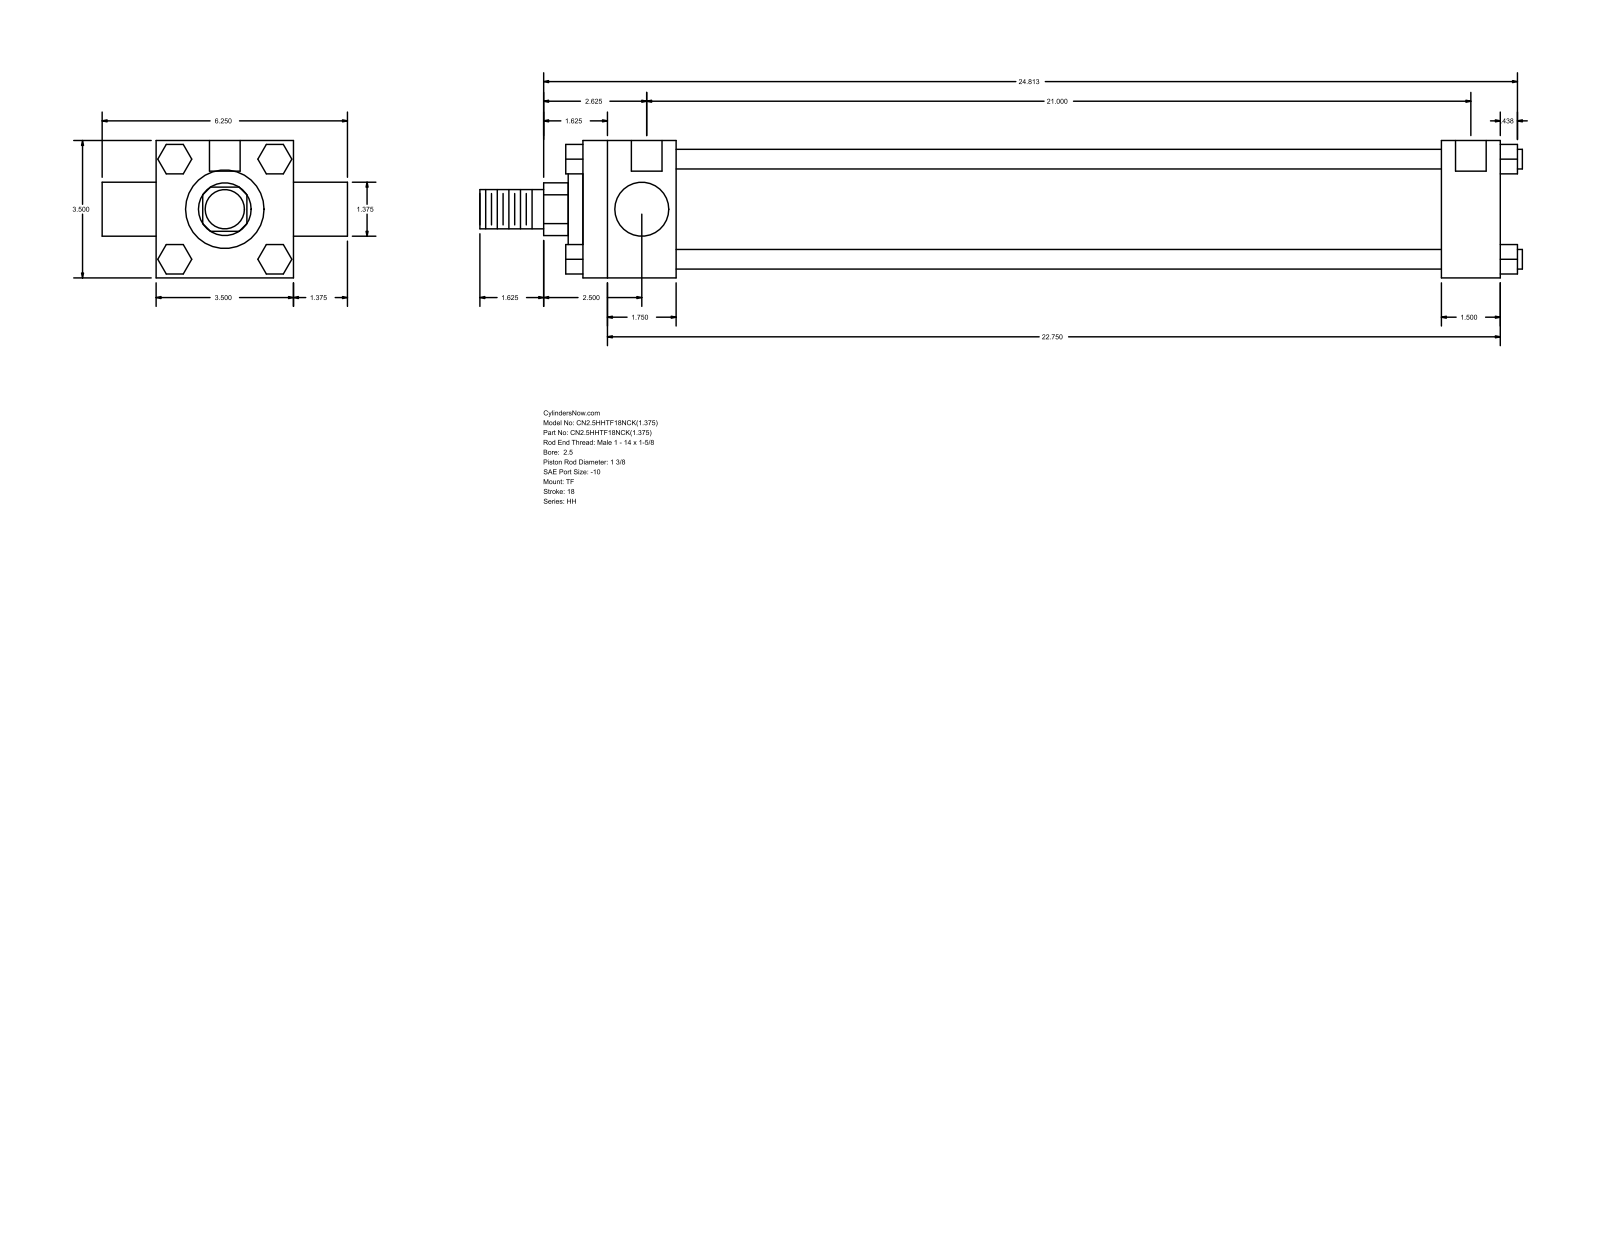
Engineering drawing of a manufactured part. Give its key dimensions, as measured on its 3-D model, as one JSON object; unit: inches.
{"part_name": "HH_TF__0250_1.375", "step_written_by": "GSSL Pune (CONFIG_CONTROL_DESIGN)", "units": "inches", "bodies": {"solids": 0, "faces": 120, "planar": 92, "cylindrical": 28, "other": 0}, "overall_size": [26.563, 6.25, 3.5], "round_holes": [[0.219, 3], [0.781, 2]], "round_bosses_or_shafts": [[0.5, 4], [1.375, 2], [2.875, 1], [2, 1], [1, 1]], "partial_cylinders_radius": [[0.672, 1]], "face_to_face_distances": [3.5, 23.375, 2.375, 21, 21.875, 19.5, 1.5, 0.75, 1.275, 2.208], "hole_center_spacings": [0.062, 21.063, 21, 21.125]}
